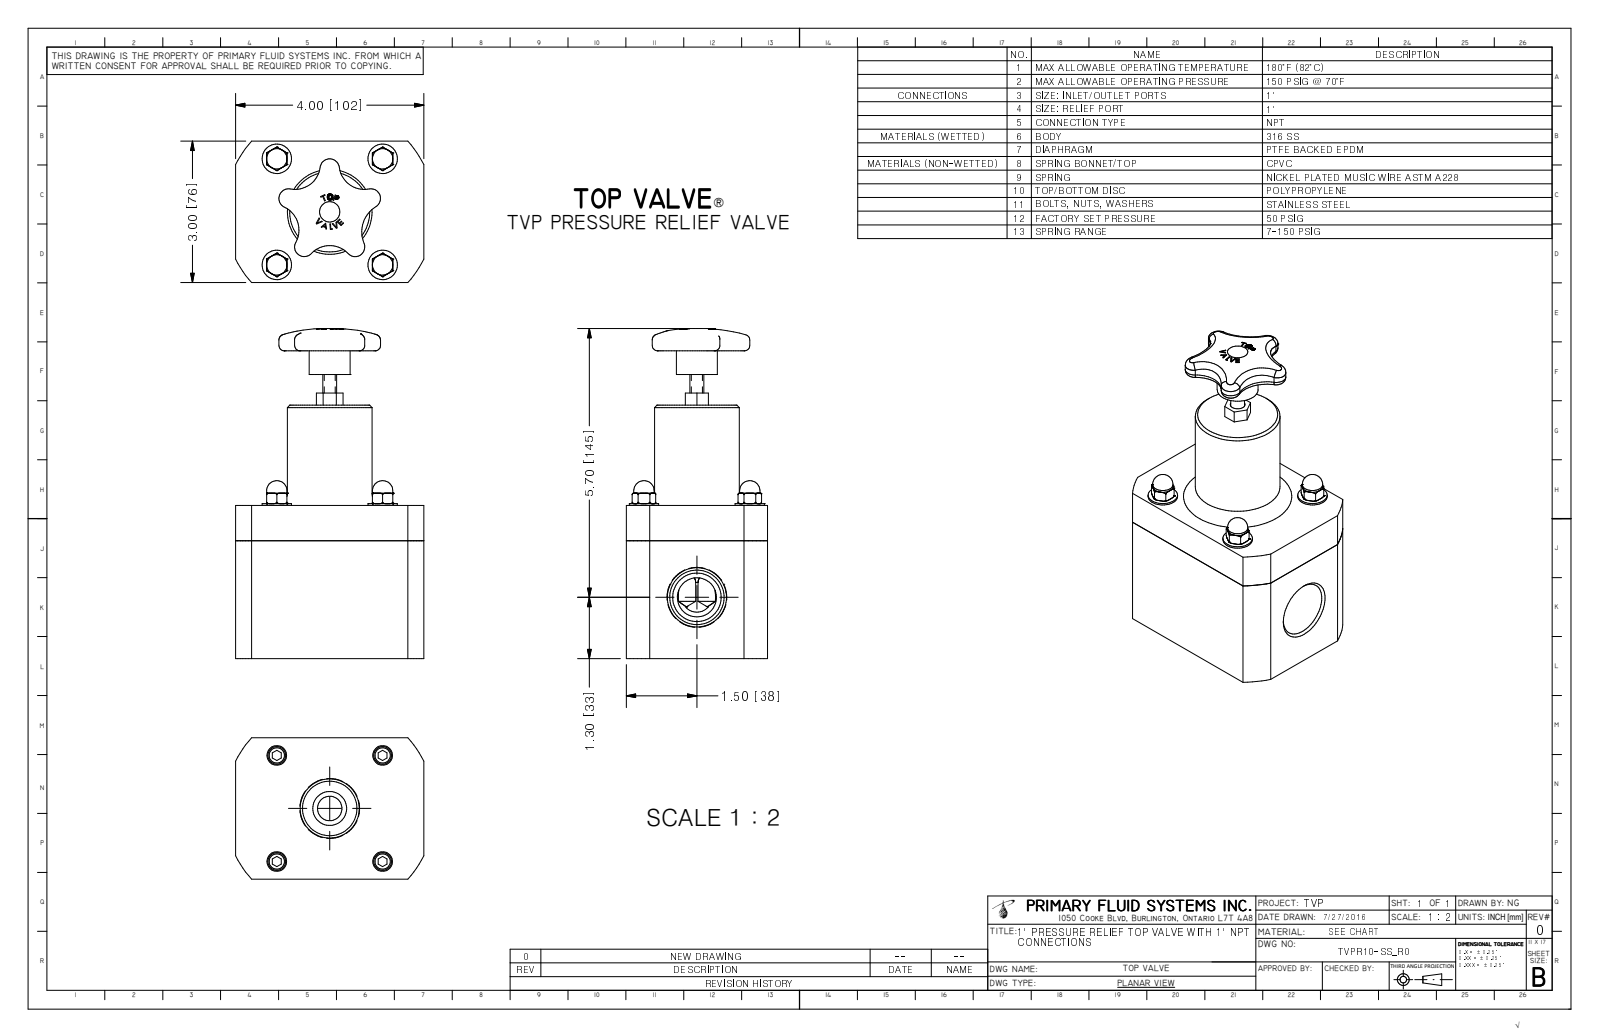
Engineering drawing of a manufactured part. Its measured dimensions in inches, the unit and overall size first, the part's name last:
Units: inches
Overall size (bounding box): 7 × 4 × 3
Round holes (diameter × count): ⌀0.175 ×4, ⌀1.156 ×2, ⌀2.525 ×1
Round bosses / shafts (diameter × count): ⌀0.625 ×4, ⌀0.433 ×4, ⌀0.375 ×4, ⌀2.5 ×1, ⌀1.8 ×1, ⌀0.87 ×1, ⌀0.293 ×1
Partial cylindrical surfaces — rounded edges, fillets, slot ends (radius × count): R0.085 ×5, R0.205 ×5, R0.536 ×4, R0.656 ×4, R0.625 ×1, R0.745 ×1, R2.238 ×1
Main face-to-face distances: 3, 3.25, 4, 1, 5.375, 2.125, 2, 0.6, 2.65, 4.775
Hole centre spacings: 2.25, 1.591, 3.182, 1.591, 1.591
Volume: 42.19 in³ · Surface area: 104.3 in²
Bodies: 1 solid, 344 faces (147 planar, 48 cylindrical, 149 other)
Part name (STEP PRODUCT): TVPR10-SS_R0
STEP written by: Autodesk Inventor 2009 (AUTOMOTIVE_DESIGN)
